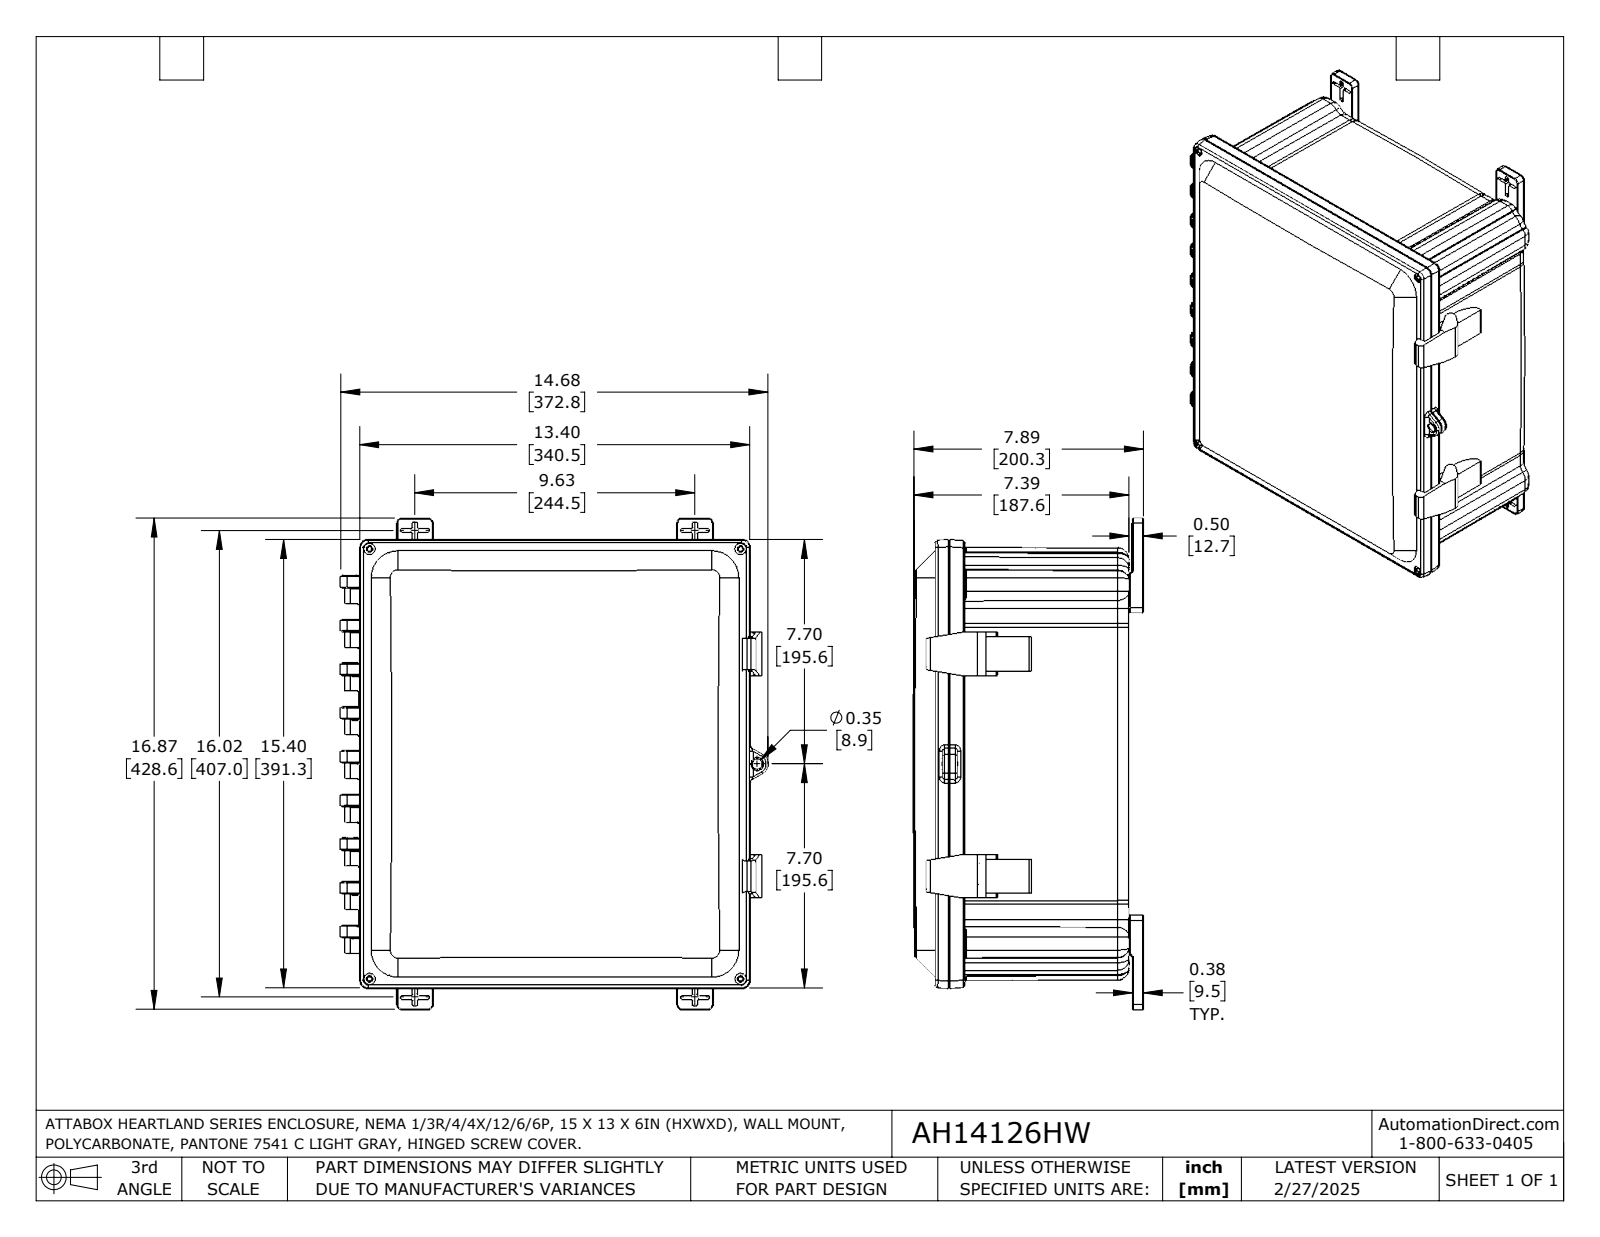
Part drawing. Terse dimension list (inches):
name: AH14126HW
written by: SolidWorks 2024 (AUTOMOTIVE_DESIGN)
unit: in
bodies: 6 solids, 2499 faces (711 planar, 783 cylindrical, 1005 other)
size: 16.875 × 14.676 × 7.888
volume: 152.1 in³; area: 1 703 in²
holes: 8× ⌀0.156, 4× ⌀0.195, 4× ⌀0.25, 4× ⌀0.313, 4× ⌀0.39, 1× ⌀0.327, 1× ⌀0.375, 1× ⌀0.45
bosses: 4× ⌀0.25, 1× ⌀0.313
rounds: 138× R0.035, 118× R0.05, 98× R0.065, 44× R0.02, 40× R0.03, 27× R0.01, 26× R0.025, 20× R0.39
face distances: 0.14, 6.14, 6, 0.5, 0.191, 6.64, 5.64, 5.5, 0.43, 1
hole spacings: 11.296, 11.568, 17.734, 0.442, 1.768, 2.21, 11.941, 12.75
